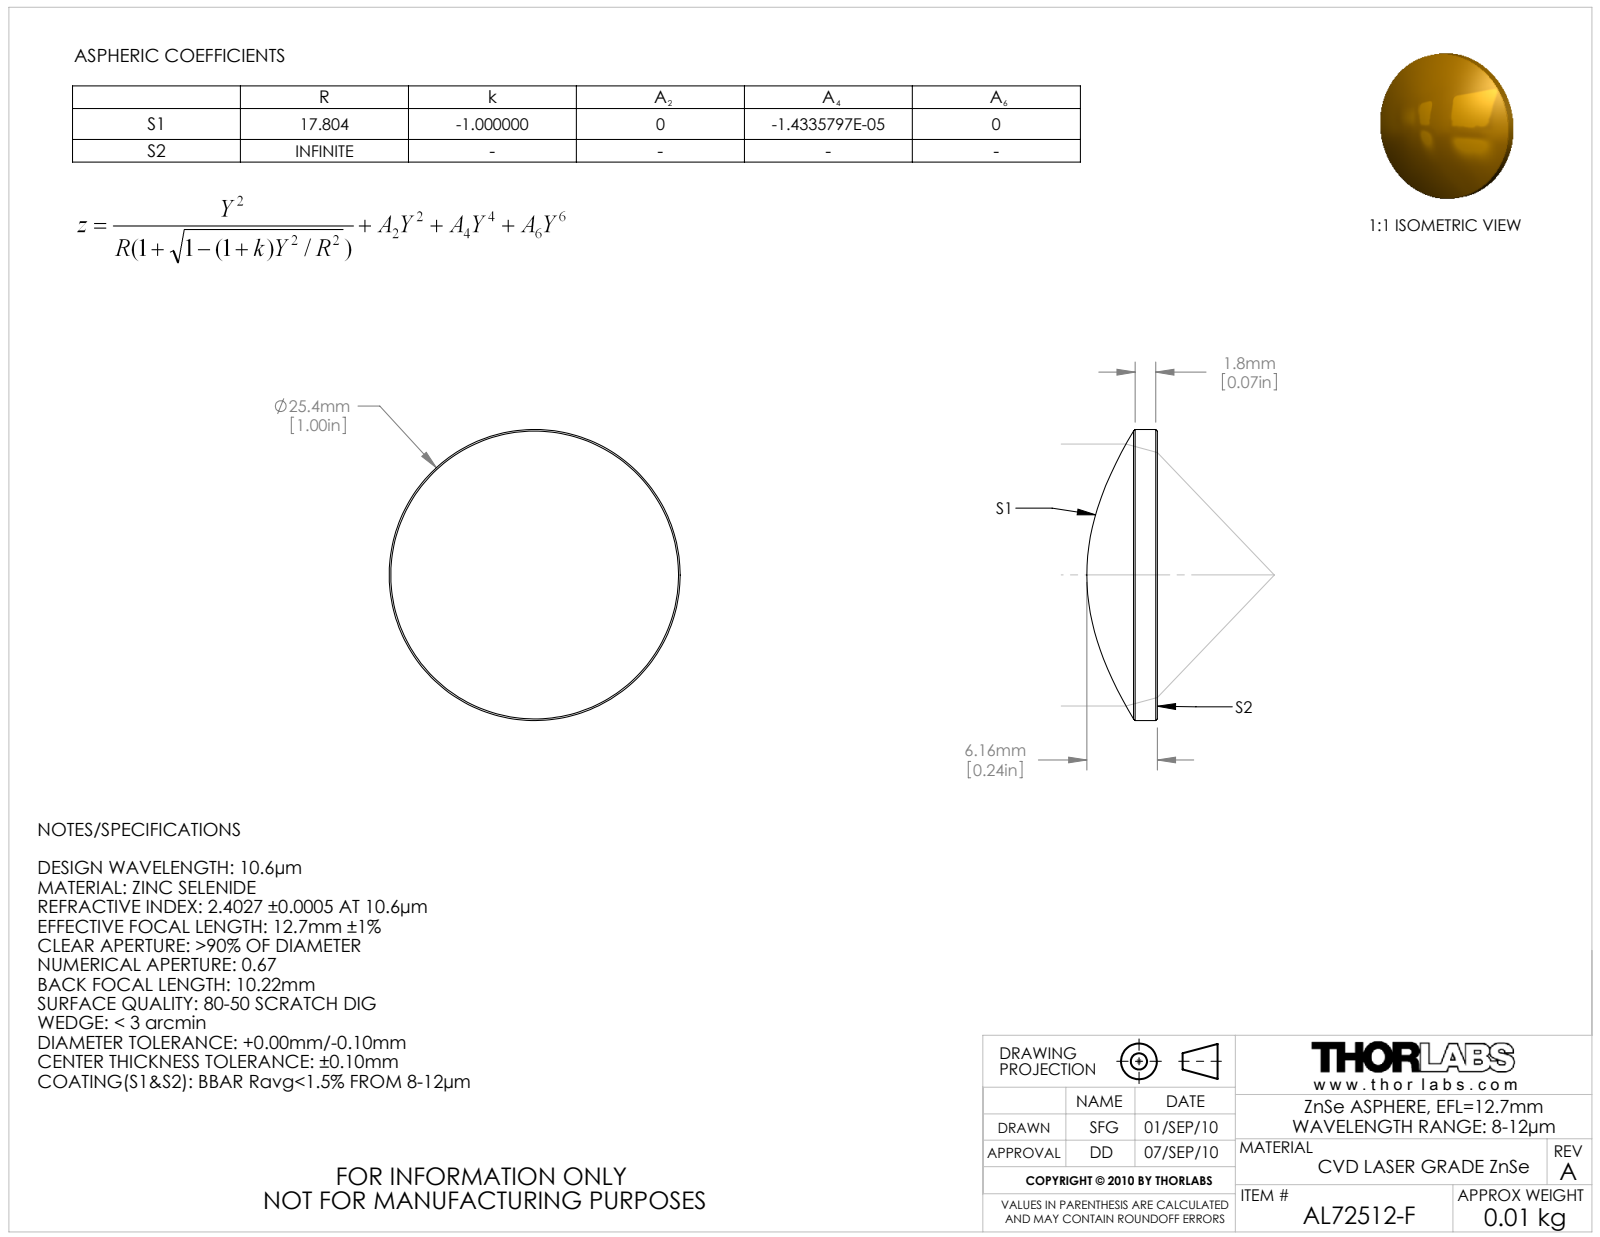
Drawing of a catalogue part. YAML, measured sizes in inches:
part_name: "21486-E0W"
step_written_by: "SolidWorks 2009 (AUTOMOTIVE_DESIGN)"
units: inches
bodies: {solids: 1, faces: 9, planar: 1, cylindrical: 2, other: 6}
overall_size: [1, 1, 0.243]
volume: 0.124
surface_area: 1.88
round_bosses_or_shafts:
  - {diameter: 1, count: 1}
